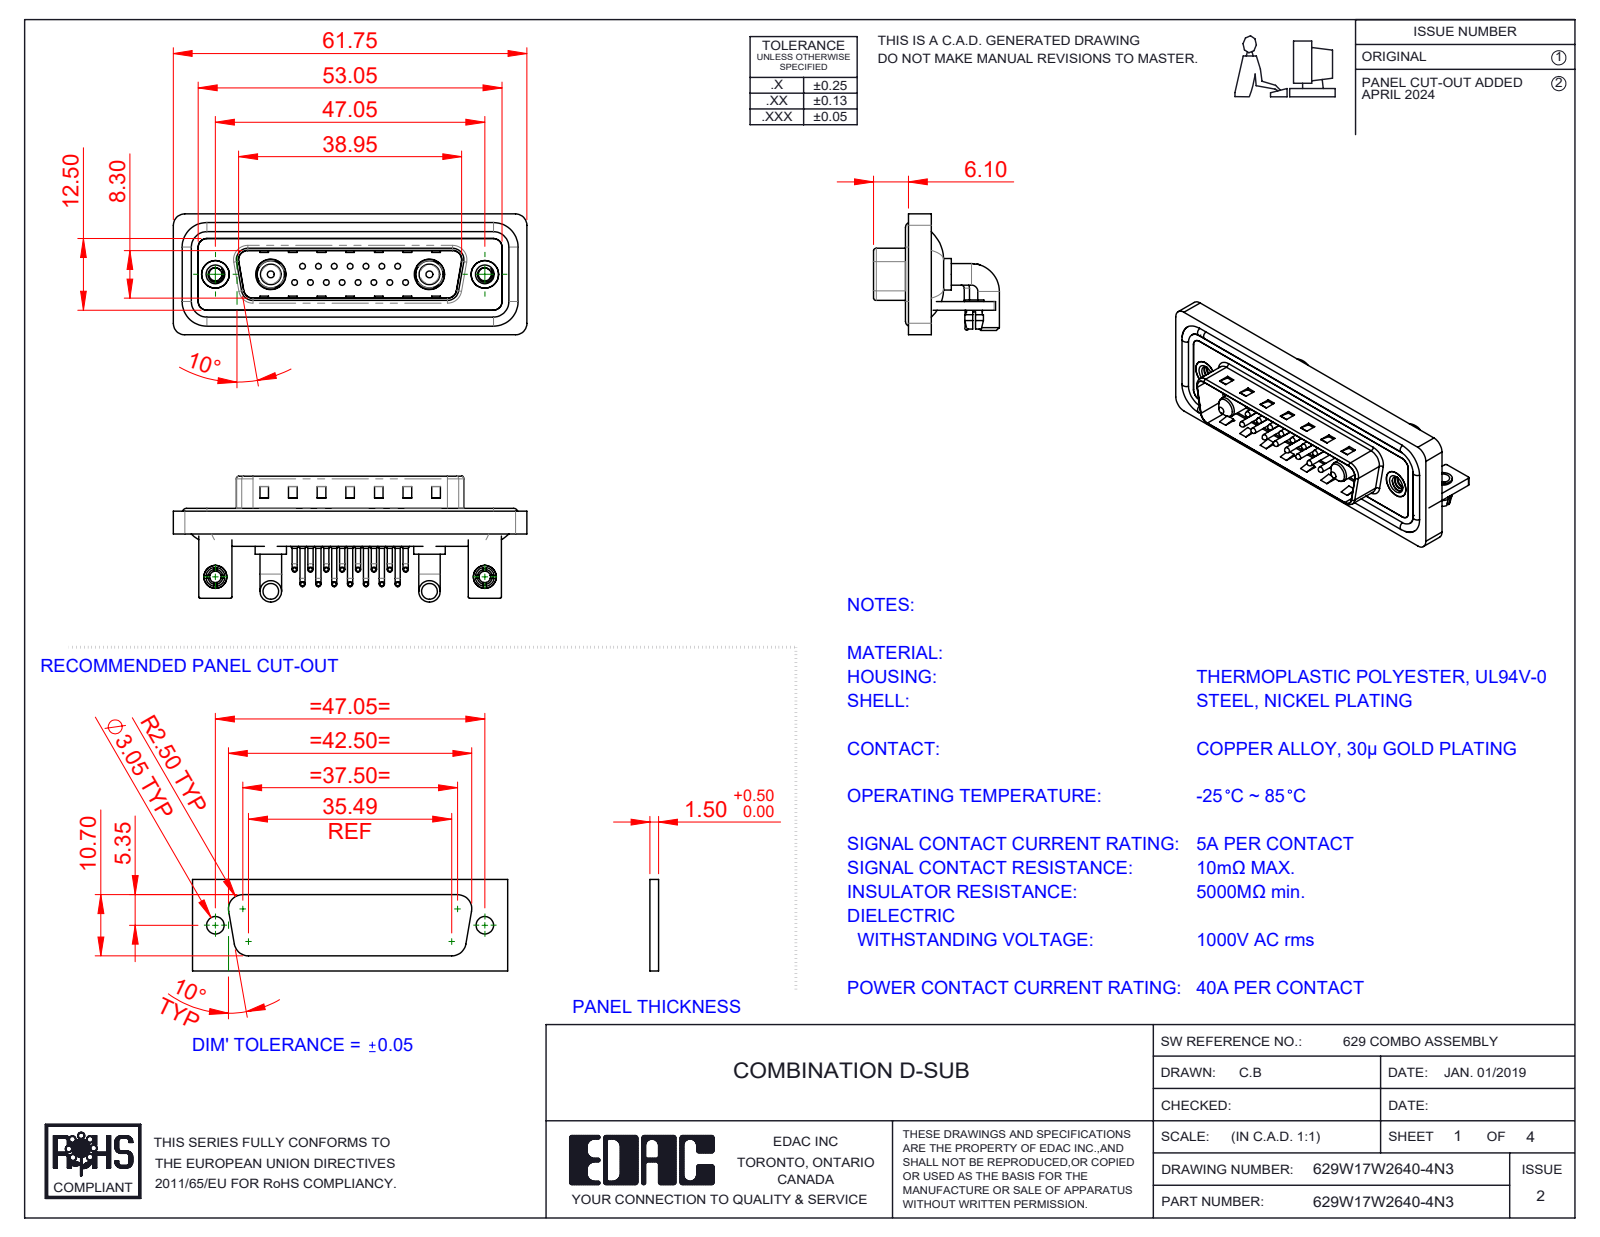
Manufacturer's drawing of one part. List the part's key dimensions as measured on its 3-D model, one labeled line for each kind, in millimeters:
Part name (STEP PRODUCT): Power Pin_40A RA; 629Combo Board Lock; 629Combo Shell Front_25 Contacts; 629Combo Waterproof Housing_25 Contacts (+7 more)
STEP written by: SolidWorks 2023 (CONFIG_CONTROL_DESIGN)
Units: millimetres
Bodies: 30 solids, 2351 faces (1257 planar, 820 cylindrical, 274 other)
Overall size (bounding box): 61.75 × 21.98 × 21.1
Volume: 7 972 mm³ · Surface area: 13 486 mm²
Round holes (diameter × count): ⌀2 ×17, ⌀0.75 ×15, ⌀1.6 ×15, ⌀2.26 ×2, ⌀2.5 ×2, ⌀3.2 ×2, ⌀4 ×2, ⌀4.8 ×2, ⌀4.85 ×2, ⌀5 ×2, ⌀5.3 ×2
Round bosses / shafts (diameter × count): ⌀0.9 ×30, ⌀1.5 ×15, ⌀1 ×15, ⌀0.65 ×15, ⌀3.75 ×4, ⌀1.6 ×4, ⌀5.5 ×2, ⌀5.2 ×2
Partial cylindrical surfaces — rounded edges, fillets, slot ends (radius × count): R2 ×19, R1.5 ×18, R0.25 ×16, R1.01 ×15, R0.5 ×9, R1.6 ×8, R0.6 ×4, R0.65 ×4
Main face-to-face distances: 0.4, 0.8, 2.1, 1.5, 2.9, 1.1, 4.1, 1.6, 4.5, 3.7
Hole centre spacings: 3.16, 2.77, 5.54, 8.31, 5.04, 7.49, 11.08, 5.03
